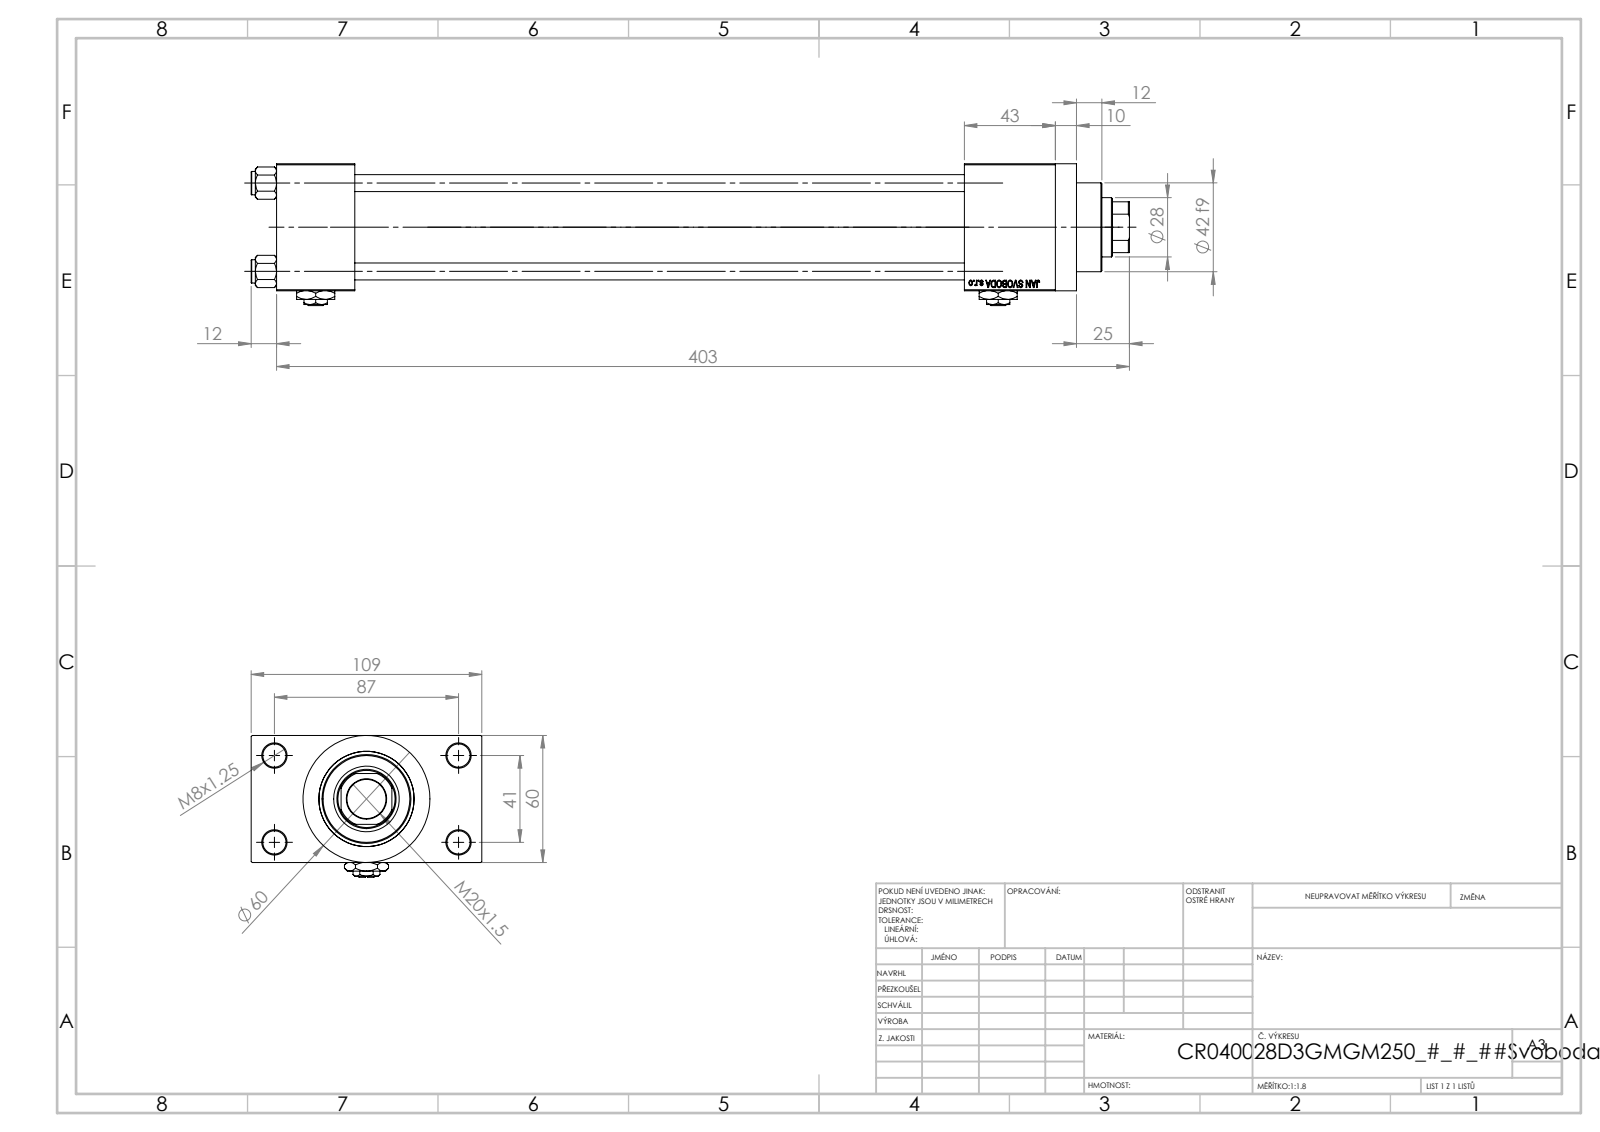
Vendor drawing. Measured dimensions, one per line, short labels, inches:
name: V215CR_D_TYCINKA; V215_VC_A; Zatka_pro_OIL_PORT; V215CR_D_Body (+2 more)
written by: SolidWorks 2019 (CONFIG_CONTROL_DESIGN)
unit: in
bodies: 13 solids, 1205 faces (546 planar, 99 cylindrical, 560 other)
size: 16.339 × 4.291 × 2.638
volume: 49.31 in³; area: 367.6 in²
holes: 4× ⌀0.315, 4× ⌀0.433, 4× ⌀0.656, 4× ⌀0.945, 3× ⌀0.276, 1× ⌀0.728, 1× ⌀1.102, 1× ⌀1.22, 1× ⌀1.575, 1× ⌀1.772
bosses: 4× ⌀0.433, 1× ⌀2.362, 1× ⌀1.811, 1× ⌀1.654
rounds: 1× R0.531
face distances: 2.362, 0.965, 11.339, 3.327, 1.457, 12.795, 14.488, 13.031, 1.693, 4.291
hole spacings: 0.892, 1.161, 1.642, 1.856, 1.893, 2.533, 3.011, 1.614
